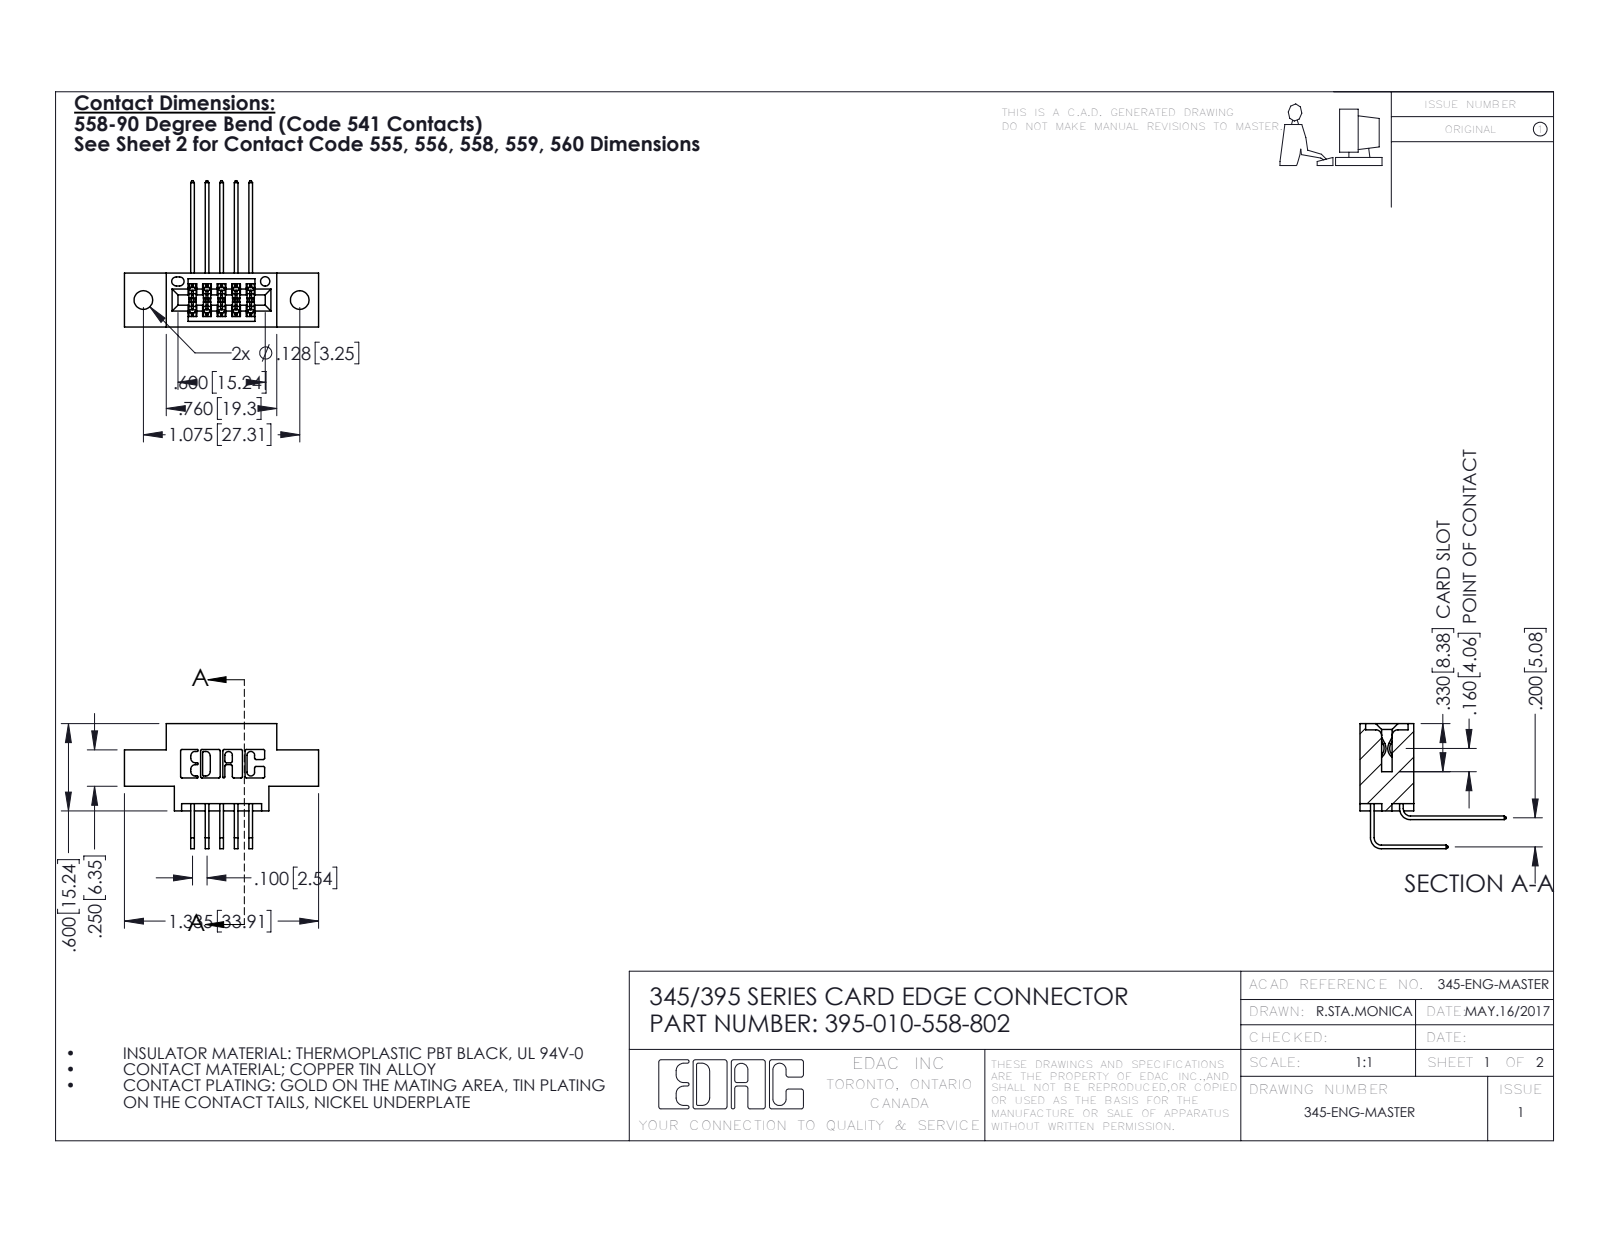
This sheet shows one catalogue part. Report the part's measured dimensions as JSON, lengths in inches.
{"part_name": "395-010-558-802; 345 Part_0.170 Offset - 0.128 Dia; 345-292-001_558 Tail - 2; 345-292-001_558 559 Tail - 1", "step_written_by": "SolidWorks 2016 (CONFIG_CONTROL_DESIGN)", "units": "inches", "bodies": {"solids": 11, "faces": 650, "planar": 434, "cylindrical": 216, "other": 0}, "overall_size": [1.335, 1.005, 0.859], "volume_in3": 0.174, "surface_area_in2": 5.658, "round_holes": [[0.128, 2], [0.064, 1]], "partial_cylinders_radius": [[0.01, 22], [0.006, 16], [0.007, 6], [0.031, 6], [0.026, 3], [0.014, 2], [0.019, 2], [0.022, 2]], "face_to_face_distances": [0.2, 0.37, 0.1, 0.072, 0.298, 0.098, 0.272, 0.025, 0.25, 0.06], "hole_center_spacings": [0.27, 0.847, 1.075]}
